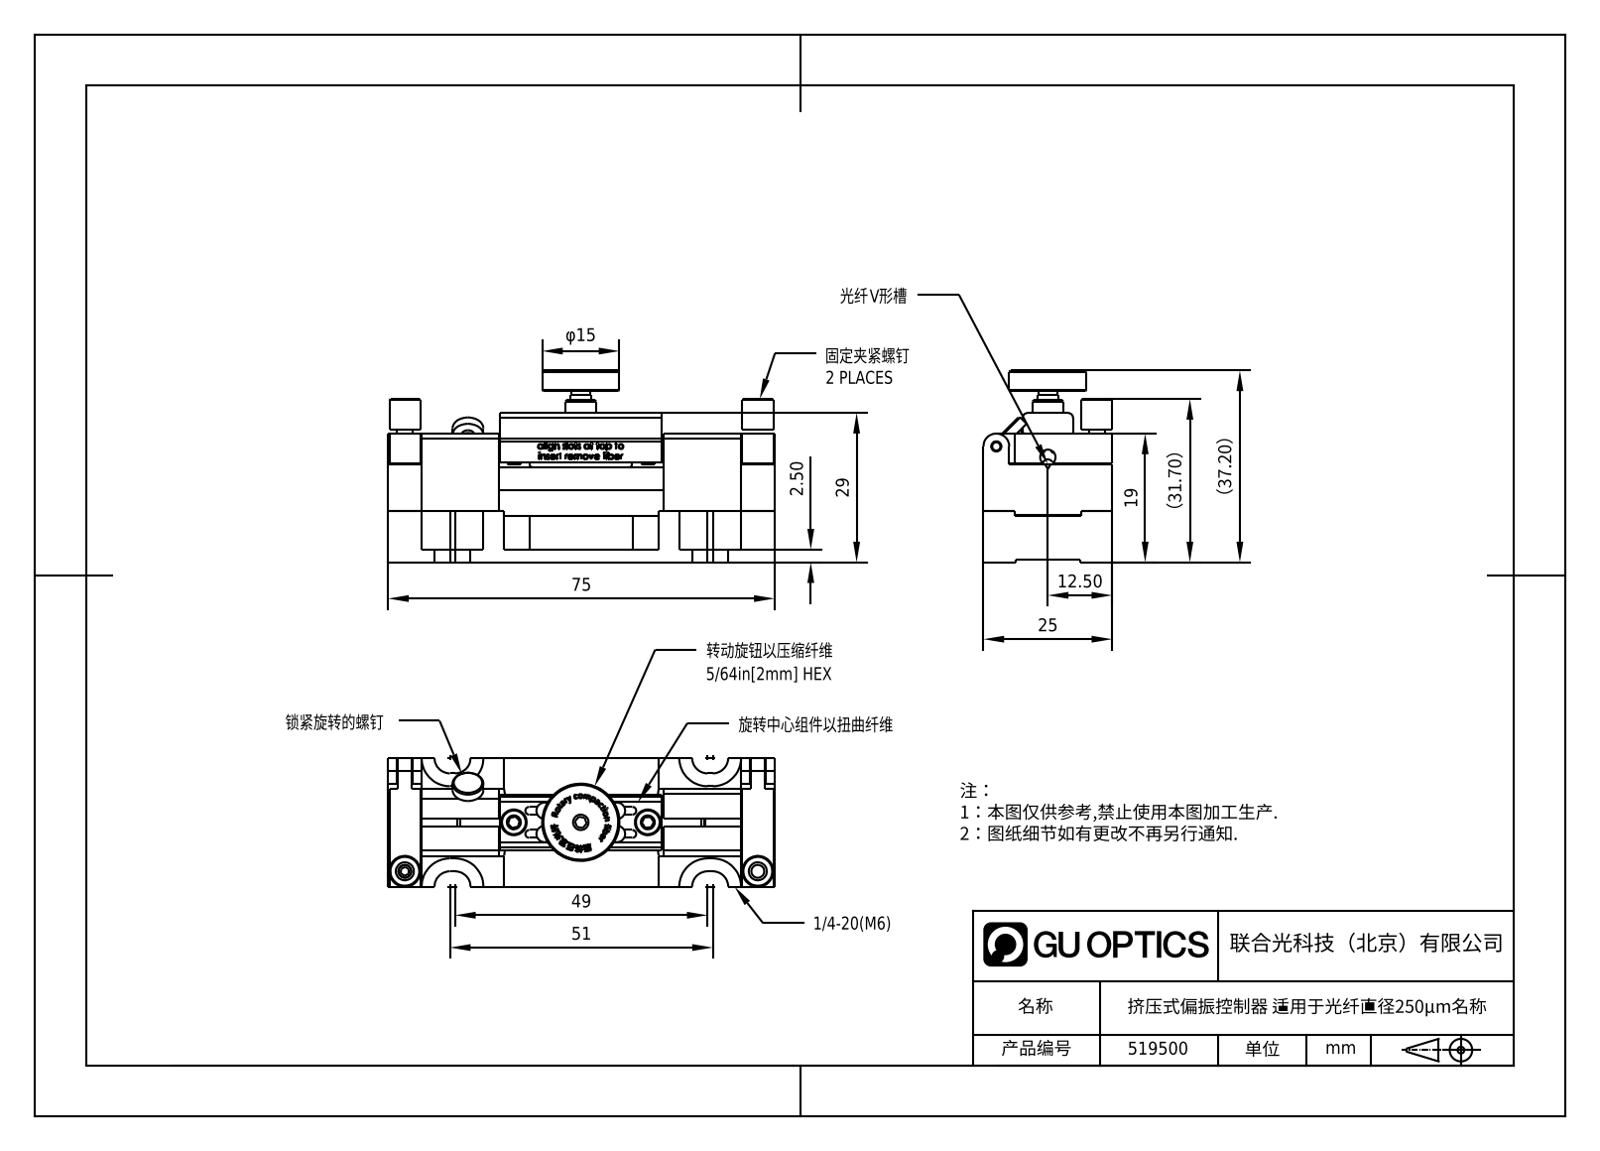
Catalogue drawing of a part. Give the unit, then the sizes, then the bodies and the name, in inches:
Units: inches
Overall size (bounding box): 2.953 × 1.665 × 0.984
Round holes (diameter × count): ⌀0.197 ×4, ⌀0.078 ×1, ⌀0.098 ×1, ⌀0.138 ×1, ⌀0.236 ×1
Round bosses / shafts (diameter × count): ⌀0.126 ×4, ⌀0.236 ×3, ⌀0.197 ×3, ⌀0.059 ×3, ⌀0.394 ×2, ⌀0.118 ×2, ⌀0.472 ×1, ⌀0.157 ×1
Partial cylindrical surfaces — rounded edges, fillets, slot ends (radius × count): R0.03 ×8, R0.118 ×8, R0.217 ×8, R0.039 ×4, R0.197 ×4, R0.016 ×2, R0.098 ×2, R0.059 ×1
Main face-to-face distances: 0.256, 0.02, 0.748, 0.236, 2.697, 0.354, 0.335, 0.079, 0.984, 0.039
Hole centre spacings: 0.315, 2.382, 0.207, 0.522, 0.831, 1.03, 1.037, 1.344
Bodies: 0 solids, 367 faces (239 planar, 77 cylindrical, 51 other)
Part name (STEP PRODUCT): 519500
STEP written by: SolidWorks 2020 (CONFIG_CONTROL_DESIGN)
